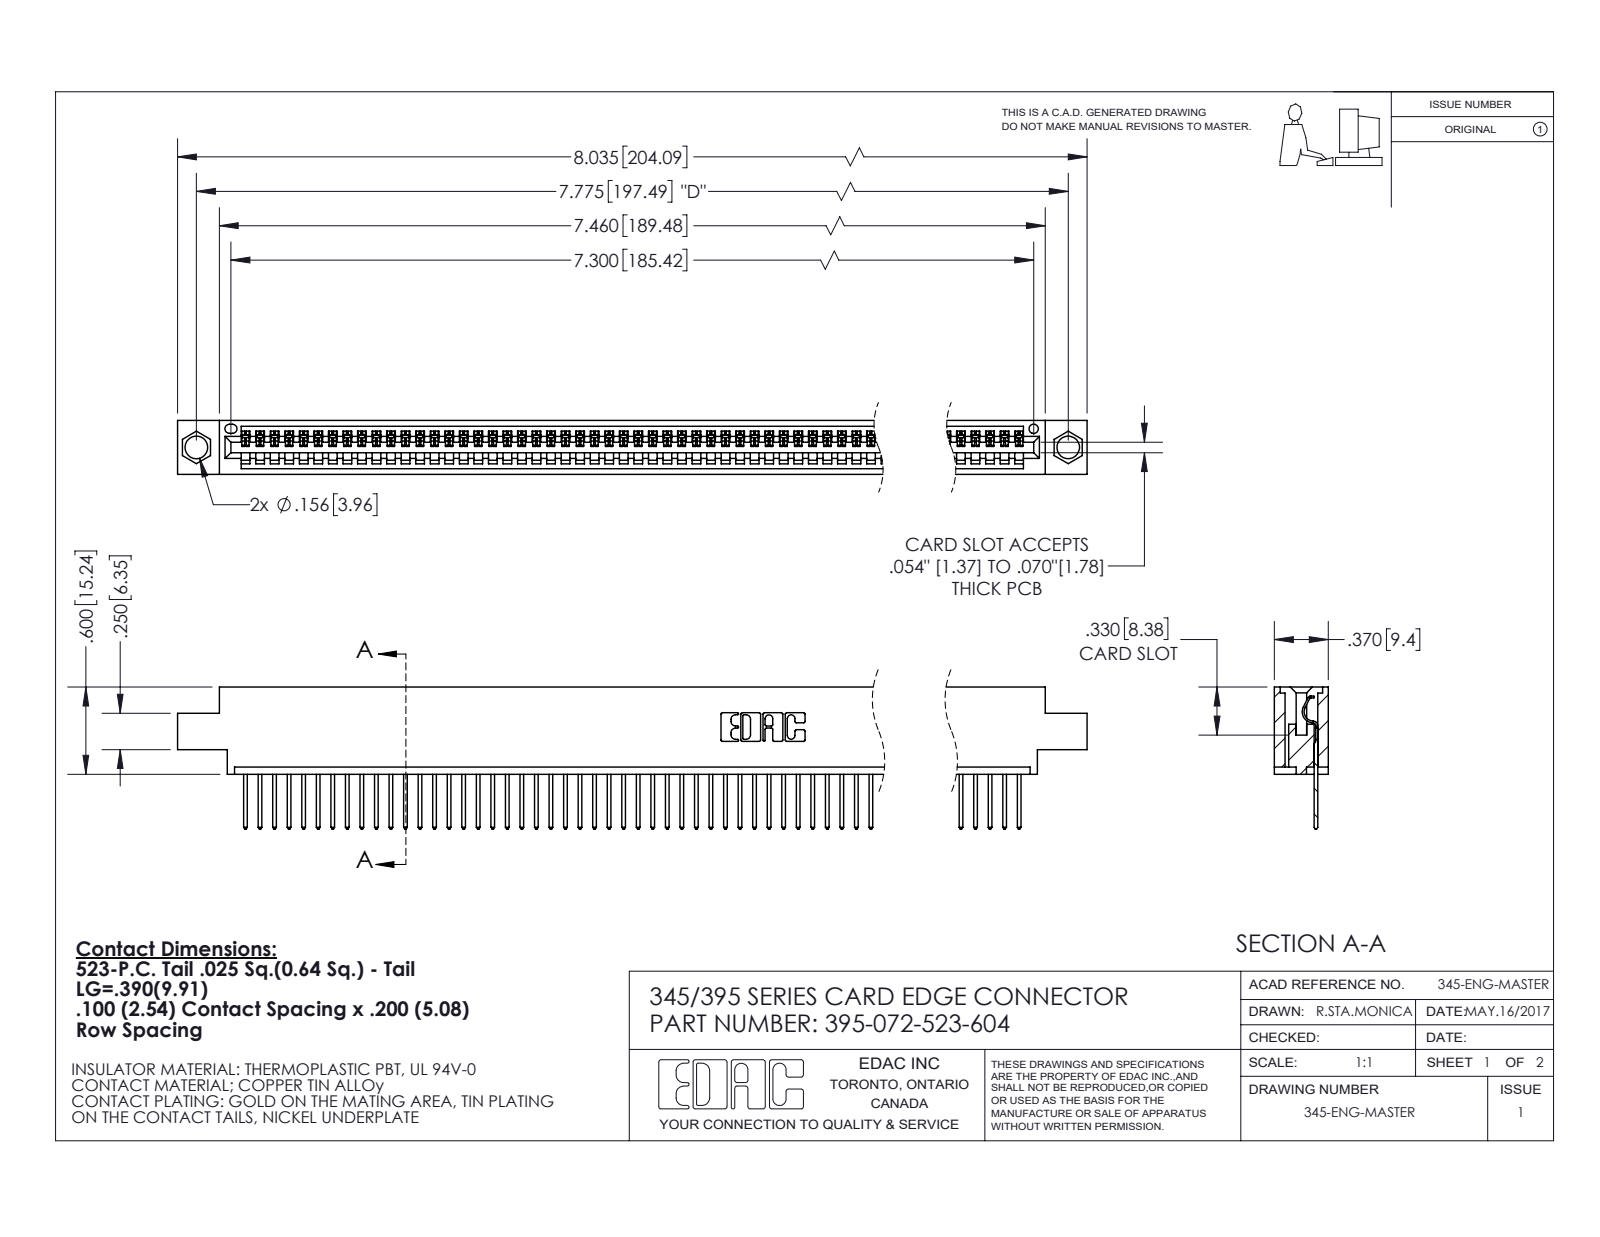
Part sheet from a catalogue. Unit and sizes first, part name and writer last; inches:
Units: inches
Overall size (bounding box): 8.035 × 0.977 × 0.37
Round holes (diameter × count): ⌀0.156 ×2, ⌀0.064 ×1
Partial cylindrical surfaces — rounded edges, fillets, slot ends (radius × count): R0.006 ×144, R0.01 ×144, R0.01 ×22, R0.007 ×6, R0.031 ×6, R0.026 ×3, R0.031 ×2, R0.04 ×2
Main face-to-face distances: 0.072, 0.298, 0.37, 0.098, 0.272, 0.025, 0.2, 0.225, 0.149, 0.175
Hole centre spacings: 0.27, 7.539, 7.775
Volume: 1.183 in³ · Surface area: 40.63 in²
Bodies: 73 solids, 4320 faces (2978 planar, 1342 cylindrical, 0 other)
Part name (STEP PRODUCT): 395-072-523-604; 345 Part_0.170 Offset - 0.156 Dia-TI; 345-292-001_345-293-123
STEP written by: SolidWorks 2020 (CONFIG_CONTROL_DESIGN)
